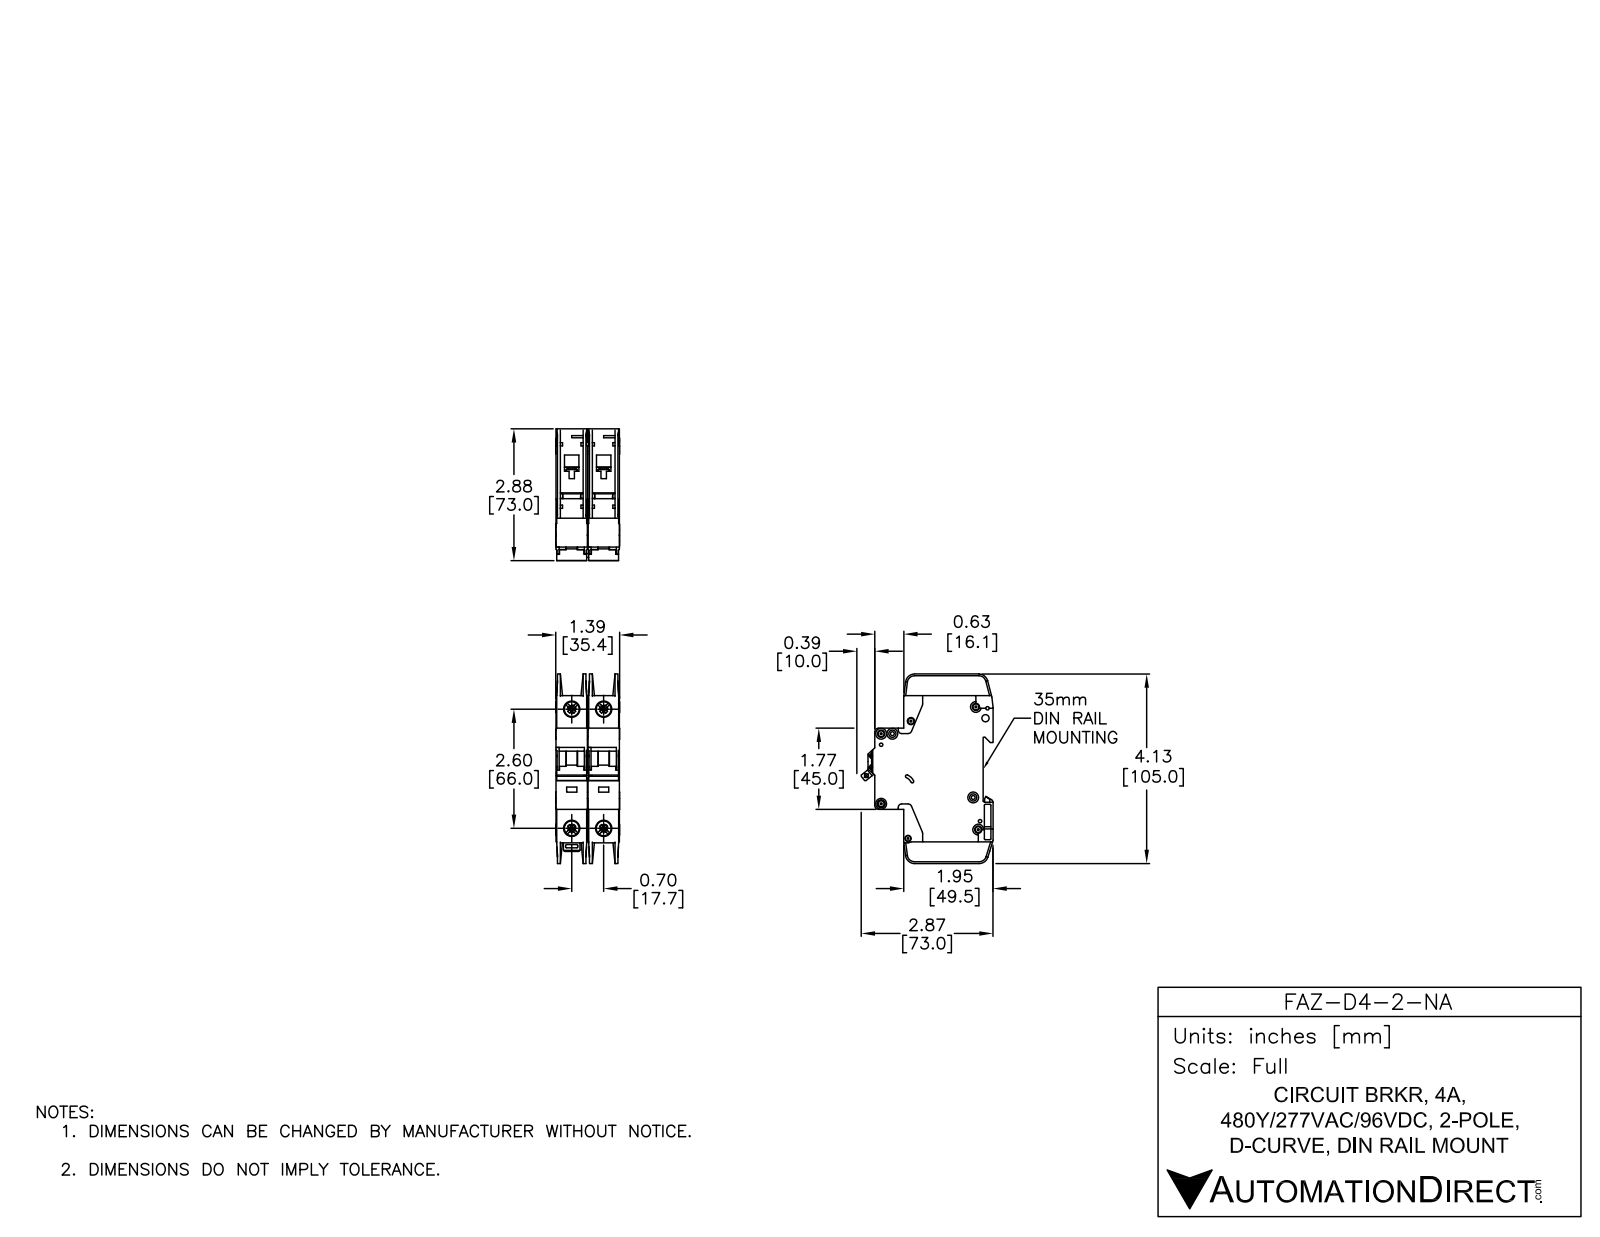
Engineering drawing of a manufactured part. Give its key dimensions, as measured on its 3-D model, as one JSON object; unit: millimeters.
{"part_name": "FAZ-D4-2-NA", "step_written_by": "SolidWorks 2014 (AUTOMOTIVE_DESIGN)", "units": "millimeters", "bodies": {"solids": 6, "faces": 1568, "planar": 818, "cylindrical": 526, "other": 224}, "overall_size": [105, 73.04, 35.4], "volume_mm3": 155390, "surface_area_mm2": 49479, "round_holes": [[3.6, 7], [7.15, 4], [8.2, 4], [1.09, 2], [1.5, 2], [4, 2], [1.9, 1], [2.15, 1], [2.2, 1], [2.55, 1], [3.3, 1], [3.4, 1]], "round_bosses_or_shafts": [[6, 7], [2.5, 2]], "partial_cylinders_radius": [[0.25, 47], [0.5, 24], [1, 18], [2, 12], [5, 5], [1.8, 4], [4, 4], [0.2, 2]], "face_to_face_distances": [17.7, 17.5, 0.7, 15.05, 2.45, 1.75, 15.75, 13.3, 35.2, 17], "hole_center_spacings": [6.2, 17.7, 66, 68.33, 5.19, 6.1, 8.19, 8.56]}
